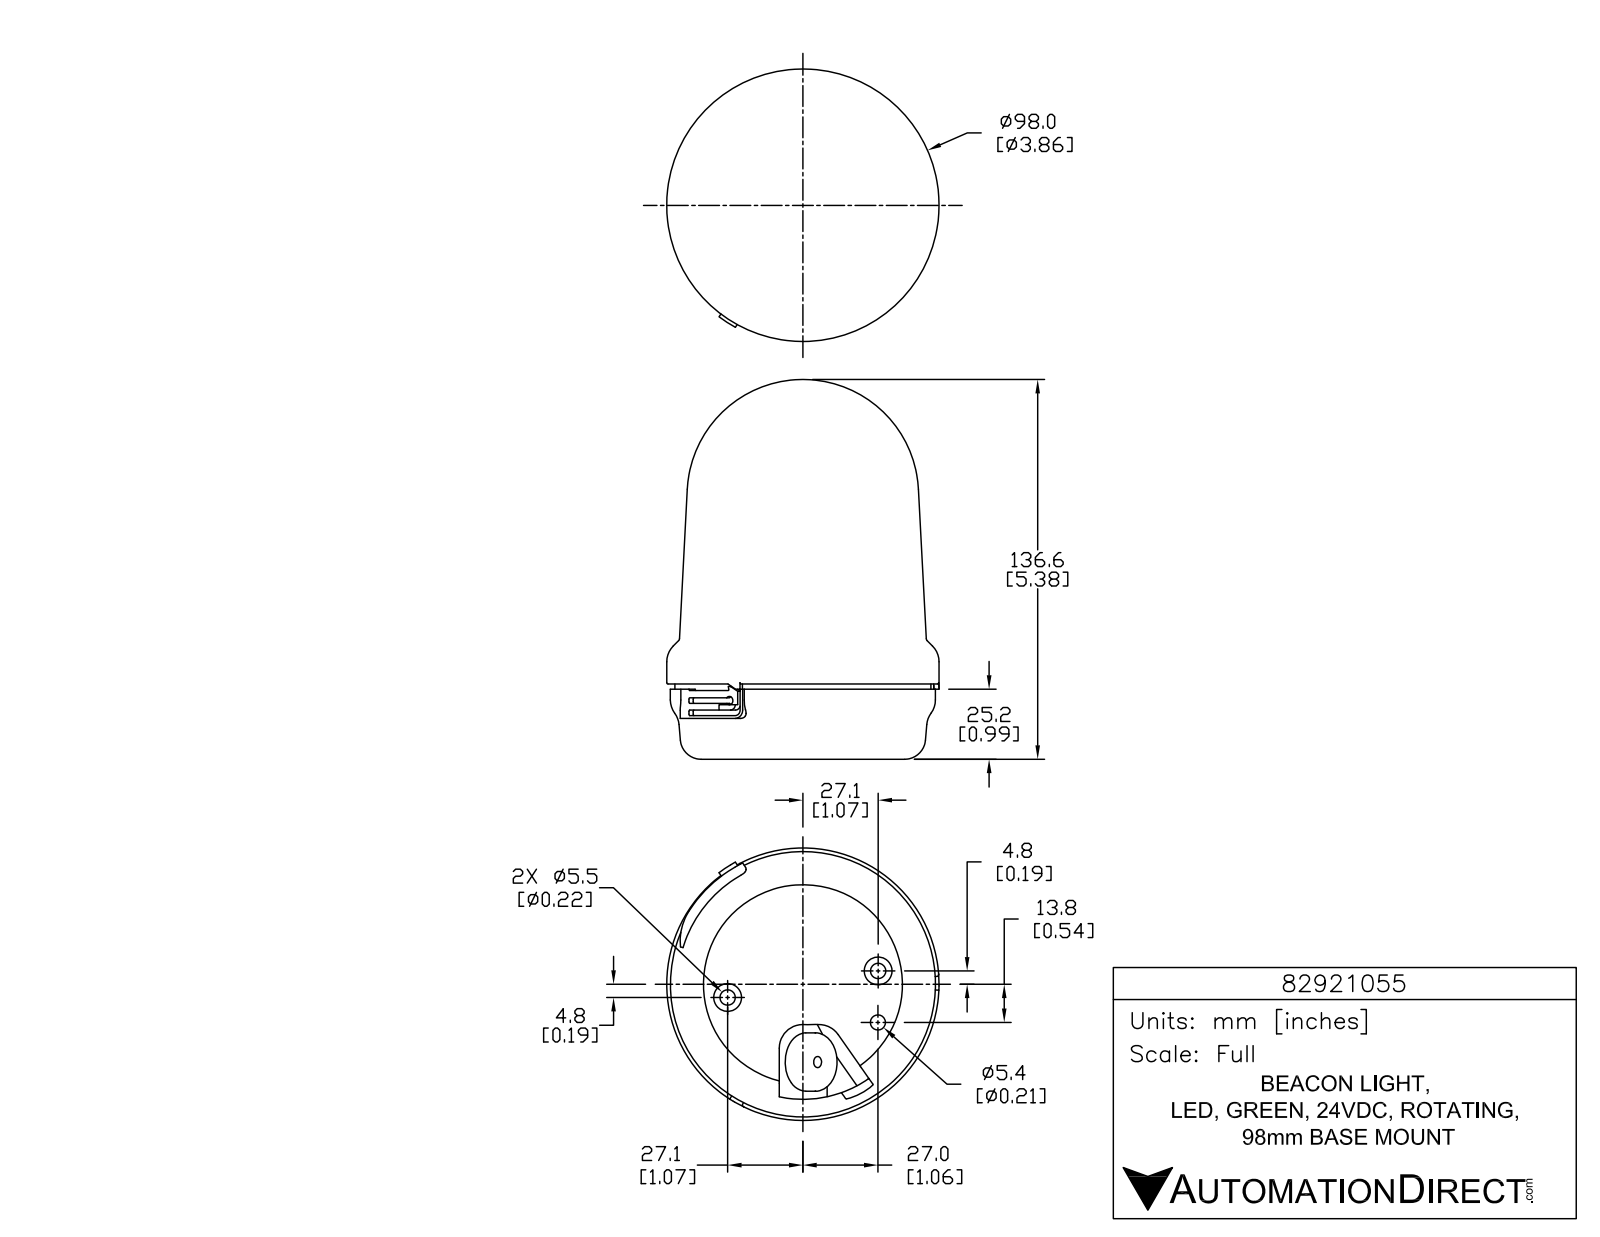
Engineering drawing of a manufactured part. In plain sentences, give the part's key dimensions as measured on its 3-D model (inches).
The part is named "82921055". Its 3-D file was written by "SolidWorks 2015 (AUTOMOTIVE_DESIGN)". It is 1 solid with 872 faces: 566 planar, 204 cylindrical and 102 other. Overall it measures 5.378 by 3.858 by 3.858 inches. Its volume is 44.69 cubic inches and its surface area 73.66 square inches. Round holes: 3 of diameter 0.059, 2 of diameter 0.217, 1 of diameter 0.157, 1 of diameter 0.213, 1 of diameter 2.819. Round bosses or shafts: 3 of diameter 0.339, 3 of diameter 0.084, 2 of diameter 0.394, 1 of diameter 3.858, 1 of diameter 3.756, 1 of diameter 3.626, 1 of diameter 0.827. Partial cylindrical surfaces (rounded edges, fillets, slot ends): 9 of radius 0.005, 6 of radius 0.005, 6 of radius 0.012, 6 of radius 0.012, 6 of radius 0.012, 6 of radius 0.196, 5 of radius 0.02, 4 of radius 0.039. The main face-to-face distances are 1.045, 0.972, 0.073, 0.02, 0.992, 1.065, 0.236, 0.579, 0.559, 0.413. The hole center spacings are 1.083, 0.73, 1.193, 2.158, 2.165.
